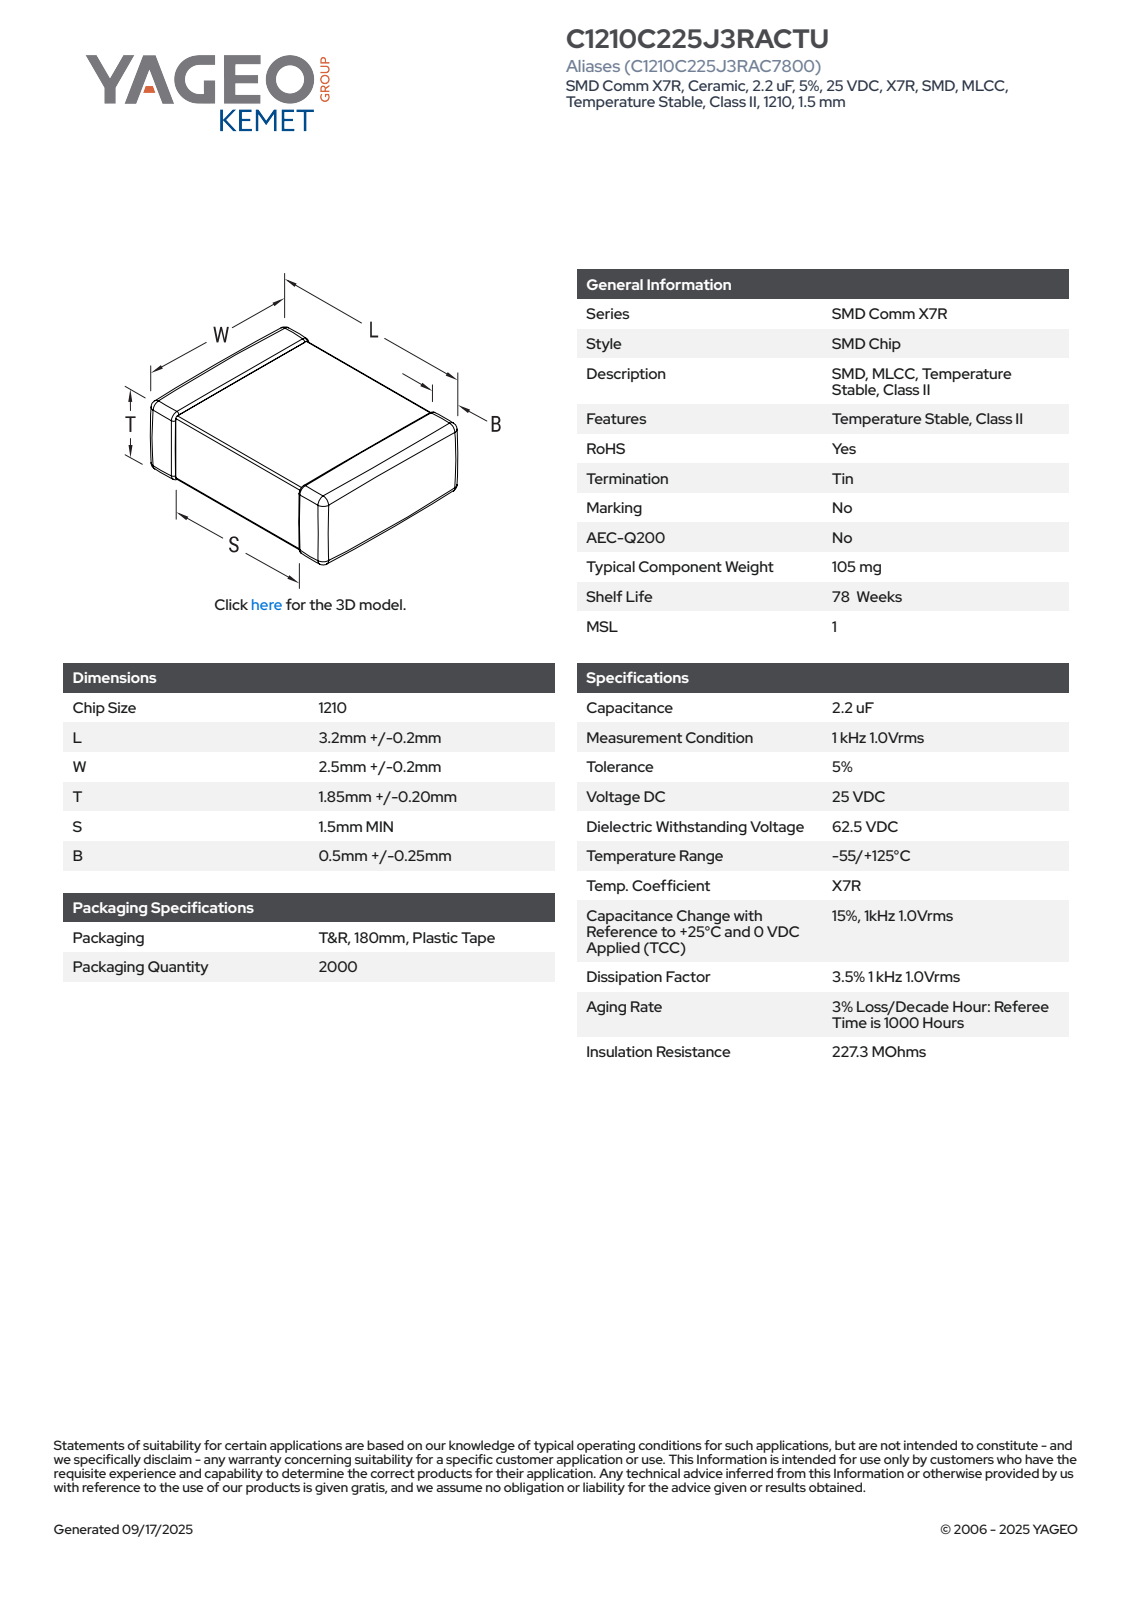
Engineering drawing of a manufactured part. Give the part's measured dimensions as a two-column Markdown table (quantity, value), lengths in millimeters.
| quantity | value |
| --- | --- |
| part name | CCS_CCSTD_1210_L3.4W2.7T2.05B0.5 |
| STEP written by | SolidWorks 2021 (AUTOMOTIVE_DESIGN) |
| units | millimeters |
| bodies | 4 solids, 125 faces (71 planar, 38 cylindrical, 16 other) |
| overall size | 3.4 × 2.7 × 2.05 |
| volume | 18 mm³ |
| surface area | 43 mm² |
| main face-to-face distances | 1.99, 3.4, 2.64, 1.93, 2.58, 2.05, 2.7, 2, 1.94, 0.4 |
